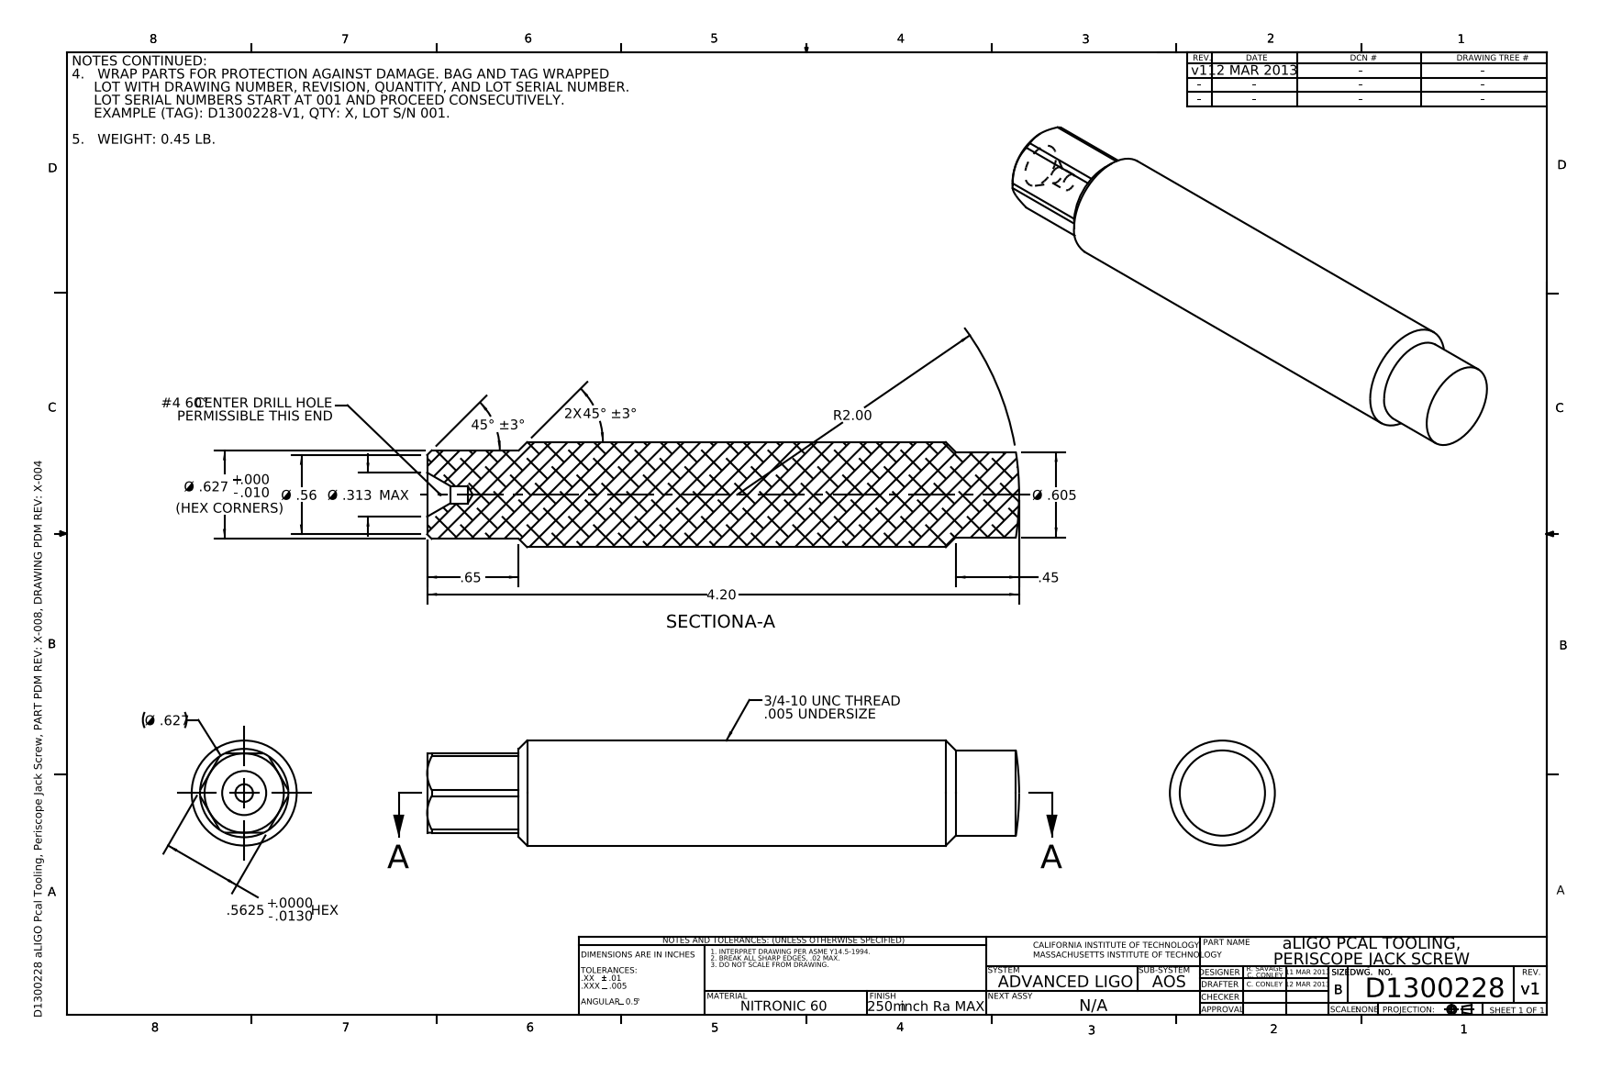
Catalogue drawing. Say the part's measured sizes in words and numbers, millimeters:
The part is named "D1300228 aLIGO Pcal Tooling, Periscope Jack Screw". Its 3-D file was written by "SolidWorks 2013 (AUTOMOTIVE_DESIGN)". It is 1 solid with 43 faces: 13 planar, 13 cylindrical and 17 other. Overall it measures 106.7 by 18.9 by 18.9 millimeters. Its volume is 26 830 cubic millimeters and its surface area 6 510 square millimeters. Round holes: 1 of diameter 3.2. Round bosses or shafts: 1 of diameter 18.9, 1 of diameter 15.4. Partial cylindrical surfaces (rounded edges, fillets, slot ends): 1 of radius 8. The main face-to-face distances are 14.3, 16.5.
